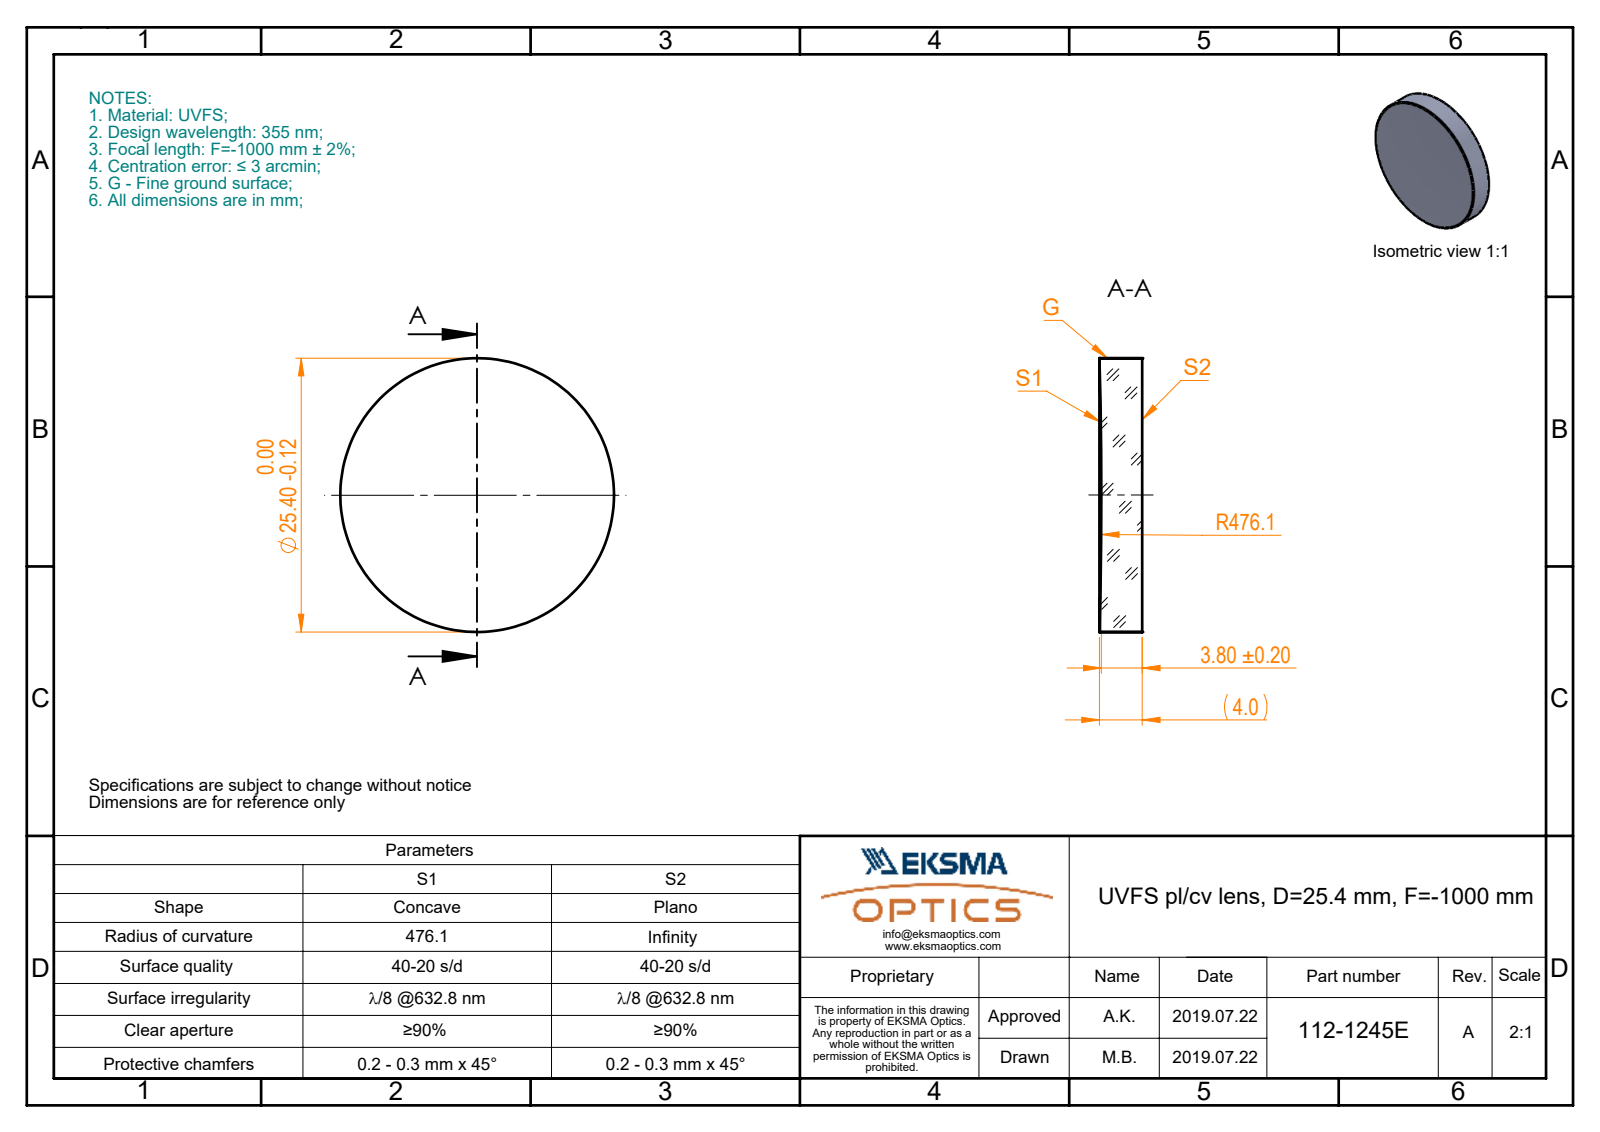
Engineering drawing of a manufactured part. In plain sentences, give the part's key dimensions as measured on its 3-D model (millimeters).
The part is named "112-1245E UVFS pl-cv 25.4 F-1000". Its 3-D file was written by "SolidWorks 2017 (CONFIG_CONTROL_DESIGN)". It is 1 solid with 5 faces: 1 planar, 2 cylindrical and 2 other. Overall it measures 25.4 by 25.4 by 3.97 millimeters. Its volume is 1 968 cubic millimeters and its surface area 1 330 square millimeters. Round bosses or shafts: 1 of diameter 25.4.
